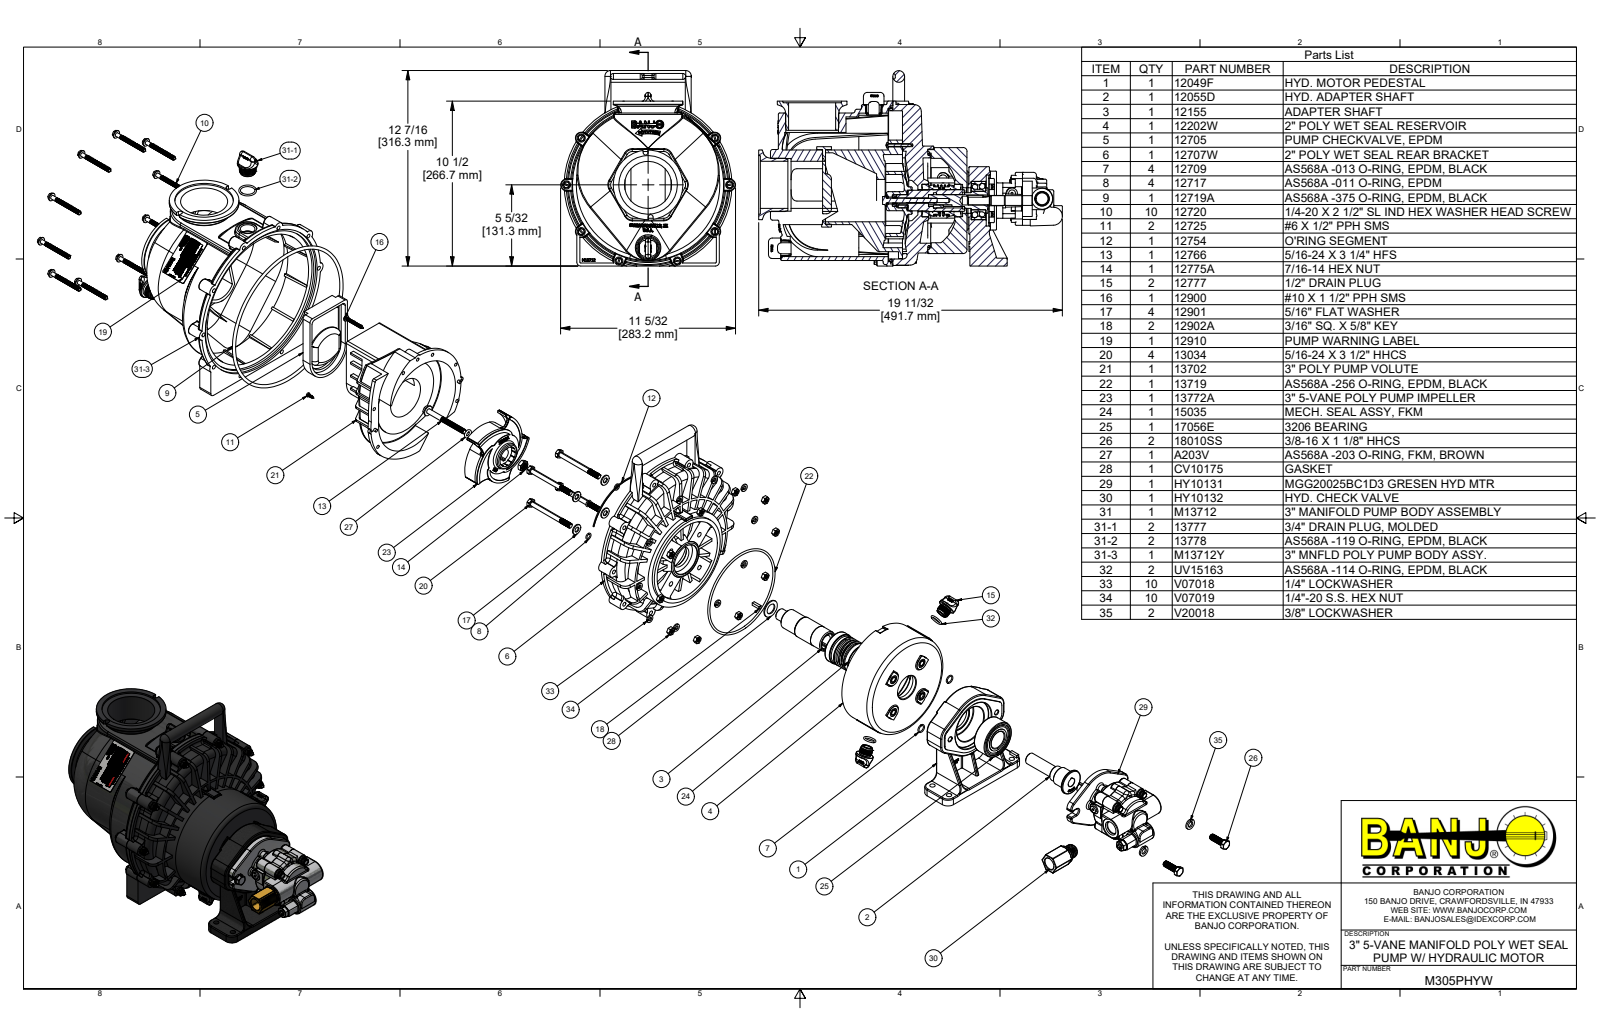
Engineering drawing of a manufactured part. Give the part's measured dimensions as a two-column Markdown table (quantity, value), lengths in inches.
| quantity | value |
| --- | --- |
| part name | M305PHYW; 12707W; 12707WX; 12703AWV (+8 more) |
| STEP written by | Autodesk Inventor 2022 (AUTOMOTIVE_DESIGN) |
| units | inches |
| bodies | 127 solids, 19052 faces (7418 planar, 3032 cylindrical, 8602 other) |
| overall size | 19.357 × 12.452 × 11.15 |
| volume | 325.7 in³ |
| surface area | 2 516 in² |
| round holes (diameter × count) | 0.196 × 10, 0.252 × 10, 0.27 × 10, 0.344 × 9, 0.469 × 8, 0.22 × 7, 0.267 × 5, 0.313 × 4, 0.561 × 4, 0.113 × 2, 0.115 × 2, 0.205 × 2 |
| round bosses / shafts (diameter × count) | 0.276 × 80, 0.324 × 34, 0.52 × 10, 0.489 × 10, 0.25 × 10, 0.312 × 8, 0.192 × 8, 0.313 × 5 |
| partial cylindrical surfaces (radius × count) | 0.03 × 200, 0.062 × 105, 0.125 × 74, 0.06 × 69, 0.015 × 55, 0.187 × 35, 0.25 × 33, 0.062 × 21 |
| main face-to-face distances | 0.25, 0.18, 1, 4.724, 0.125, 0.2, 2.88, 2.225, 2.499, 0.61 |
| hole center spacings | 5.2, 3.087, 3.128, 6.15, 0.69, 1.81, 2.5, 2.56 |
